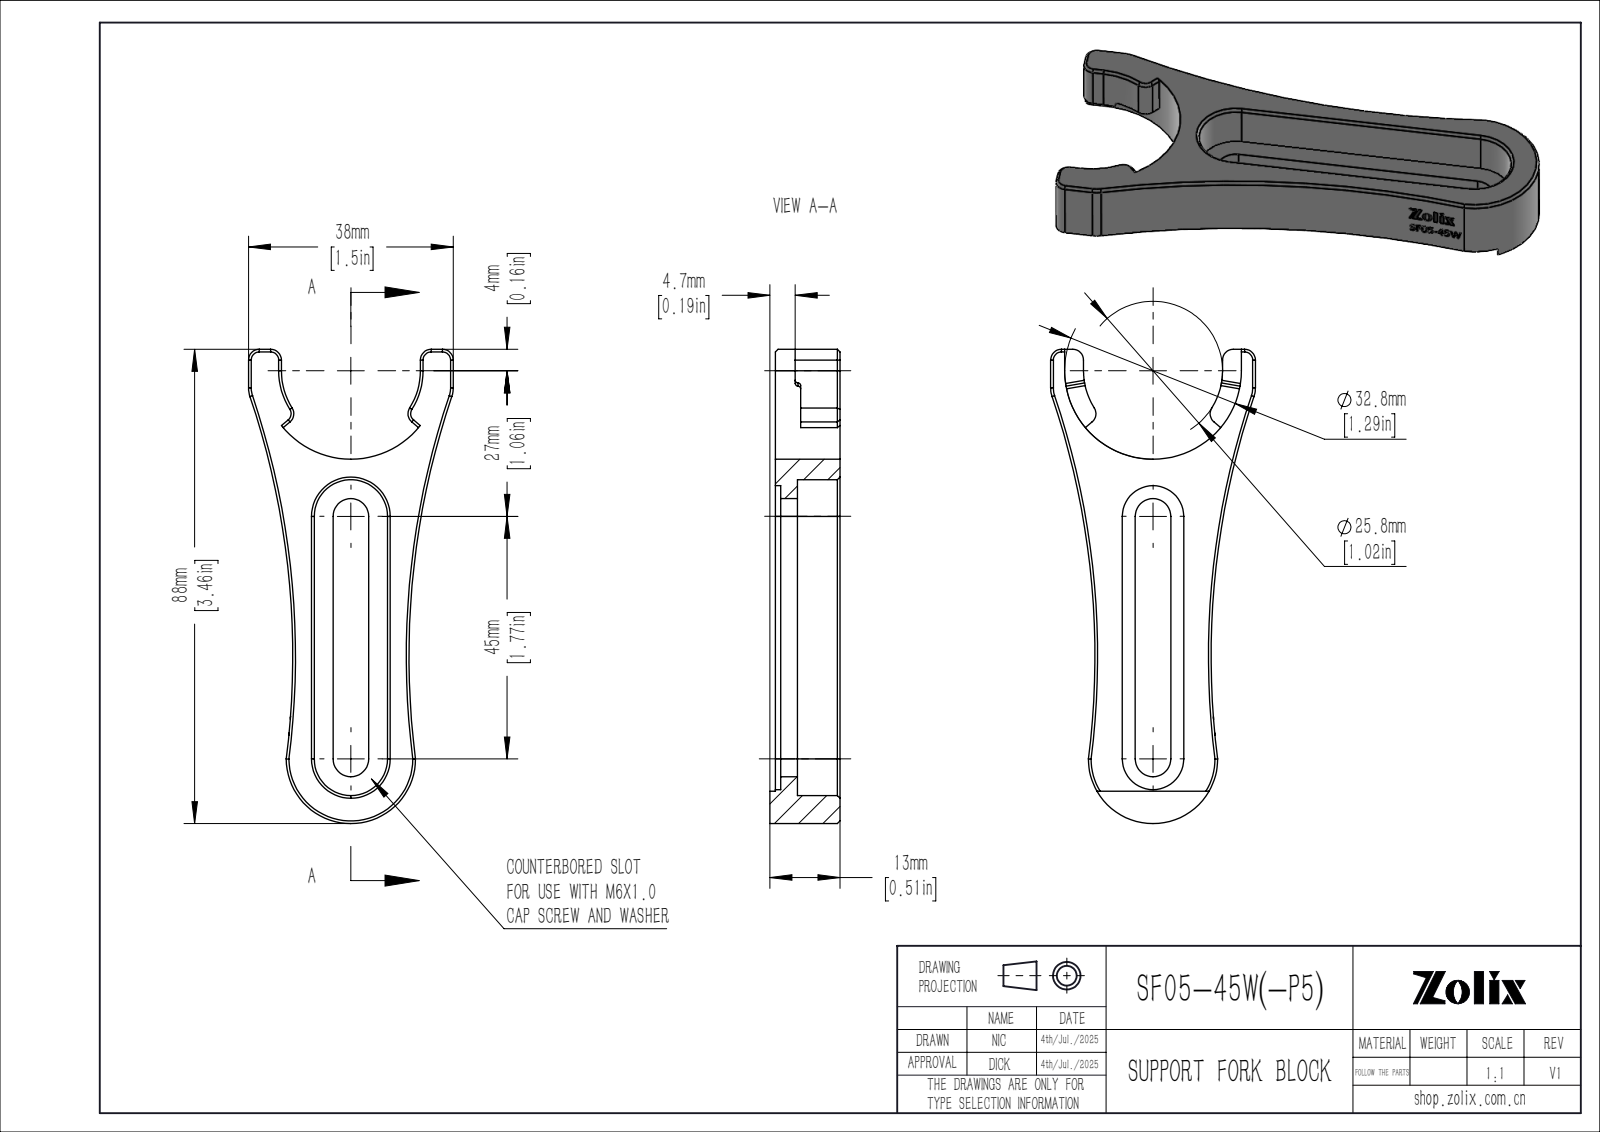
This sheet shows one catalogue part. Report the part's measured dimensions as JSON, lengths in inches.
{"part_name": "SF05-45W", "step_written_by": "SolidWorks 2020 (CONFIG_CONTROL_DESIGN)", "units": "inches", "bodies": {"solids": 1, "faces": 380, "planar": 80, "cylindrical": 49, "other": 251}, "overall_size": [3.465, 1.496, 0.512], "volume_in3": 0.843, "surface_area_in2": 11.61, "partial_cylinders_radius": [[0.079, 6], [0.02, 4], [0.13, 2], [0.197, 2], [0.224, 2], [0.268, 2], [5.906, 2], [0.472, 1]], "face_to_face_distances": [0.472, 0.161, 0.311, 0.039, 0.535, 0.138, 0.122, 0.433, 0.398, 0.26]}
